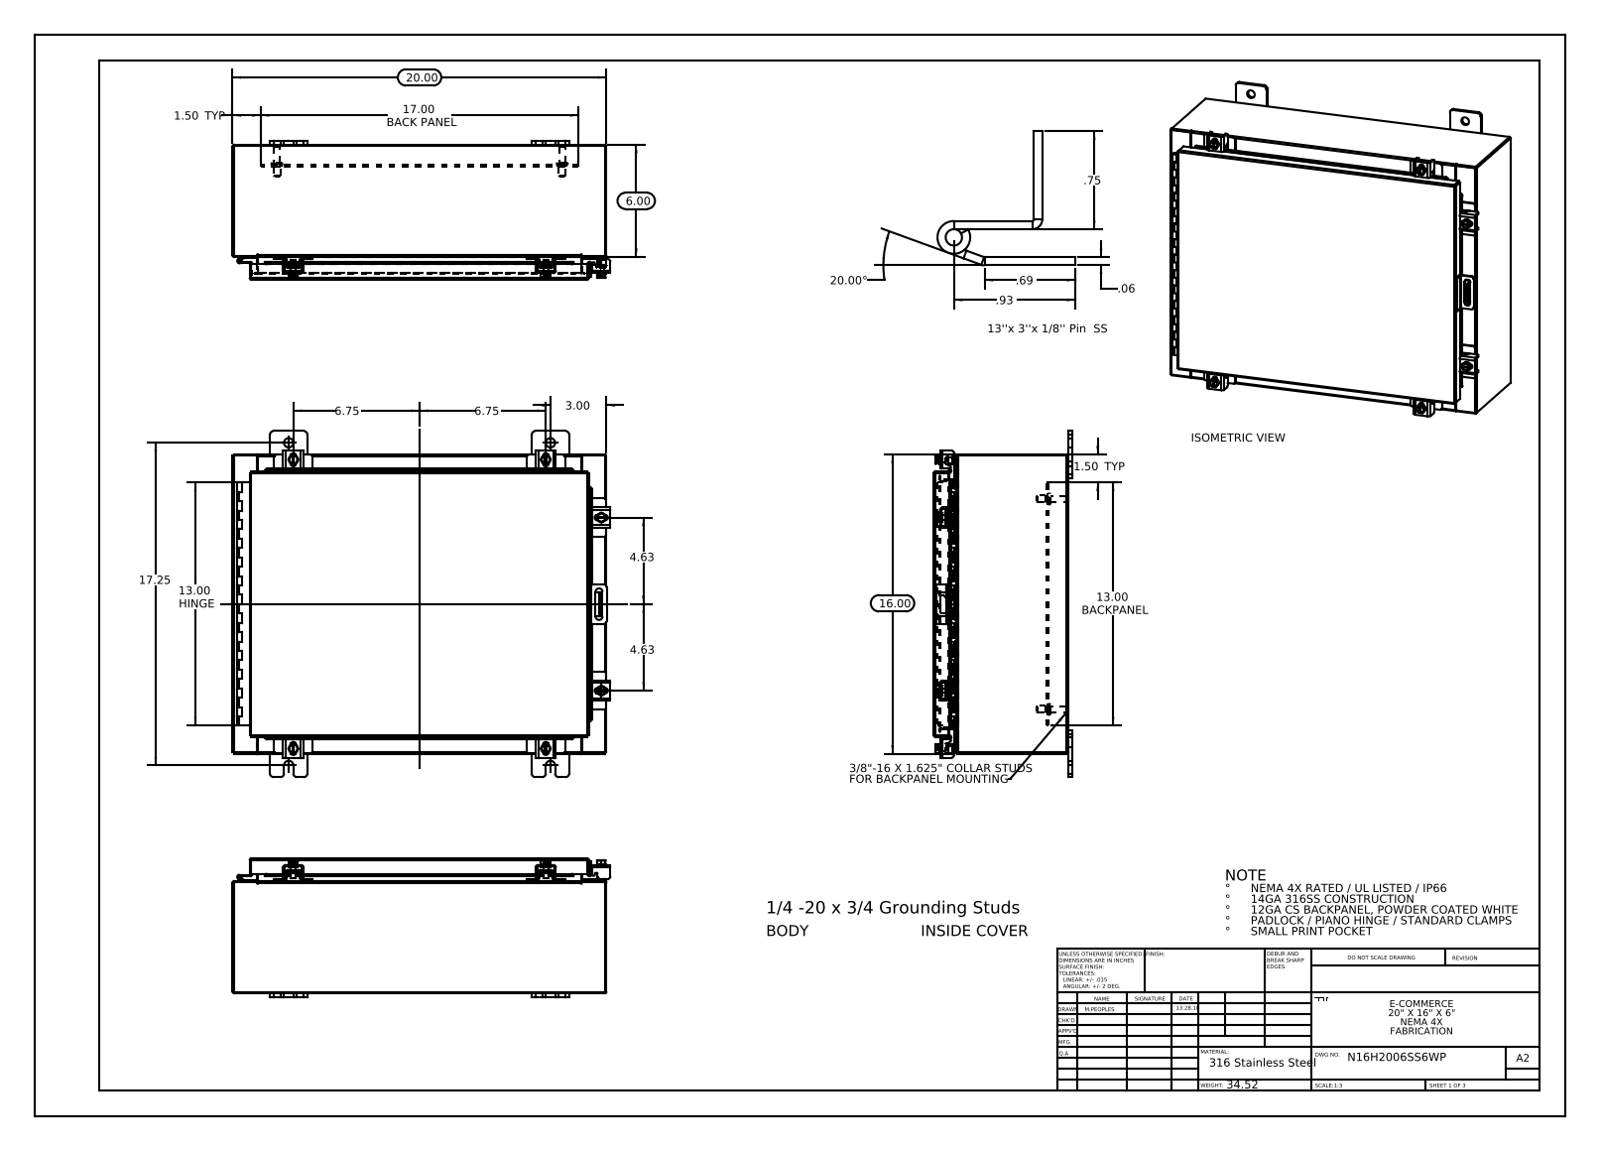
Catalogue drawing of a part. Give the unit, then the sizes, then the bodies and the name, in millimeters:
Units: millimetres
Overall size (bounding box): 513.4 × 469.9 × 187.7
Round holes (diameter × count): ⌀12.7 ×8, ⌀5.4 ×6, ⌀6.6 ×6, ⌀3.2 ×2, ⌀3.2 ×1
Round bosses / shafts (diameter × count): ⌀6.4 ×7, ⌀12.7 ×6, ⌀10.1 ×6, ⌀15.9 ×4, ⌀9.5 ×4, ⌀8.4 ×4, ⌀8 ×2, ⌀6 ×2
Partial cylindrical surfaces — rounded edges, fillets, slot ends (radius × count): R1.5 ×30, R4.8 ×24, R0.3 ×23, R2.2 ×21, R3 ×12, R3.6 ×12, R3.2 ×10, R1.3 ×9
Main face-to-face distances: 1.9, 181, 179.1, 182.9, 404.5, 25.4, 27.3, 153.7, 155.6, 29.9
Hole centre spacings: 339.9, 498.3, 10.9, 23.7, 47.2, 57.8, 57.8, 59.1
Volume: 2 002 000 mm³ · Surface area: 1 992 000 mm²
Bodies: 49 solids, 1527 faces (806 planar, 613 cylindrical, 108 other)
Part name (STEP PRODUCT): N16H2006SS6WP; N16H2006SS6WP Padlock Staple; N16H2006SS6WP Standard Clamps; N16H2006SS6WP Cover (+8 more)
STEP written by: SolidWorks 2013 (CONFIG_CONTROL_DESIGN)
